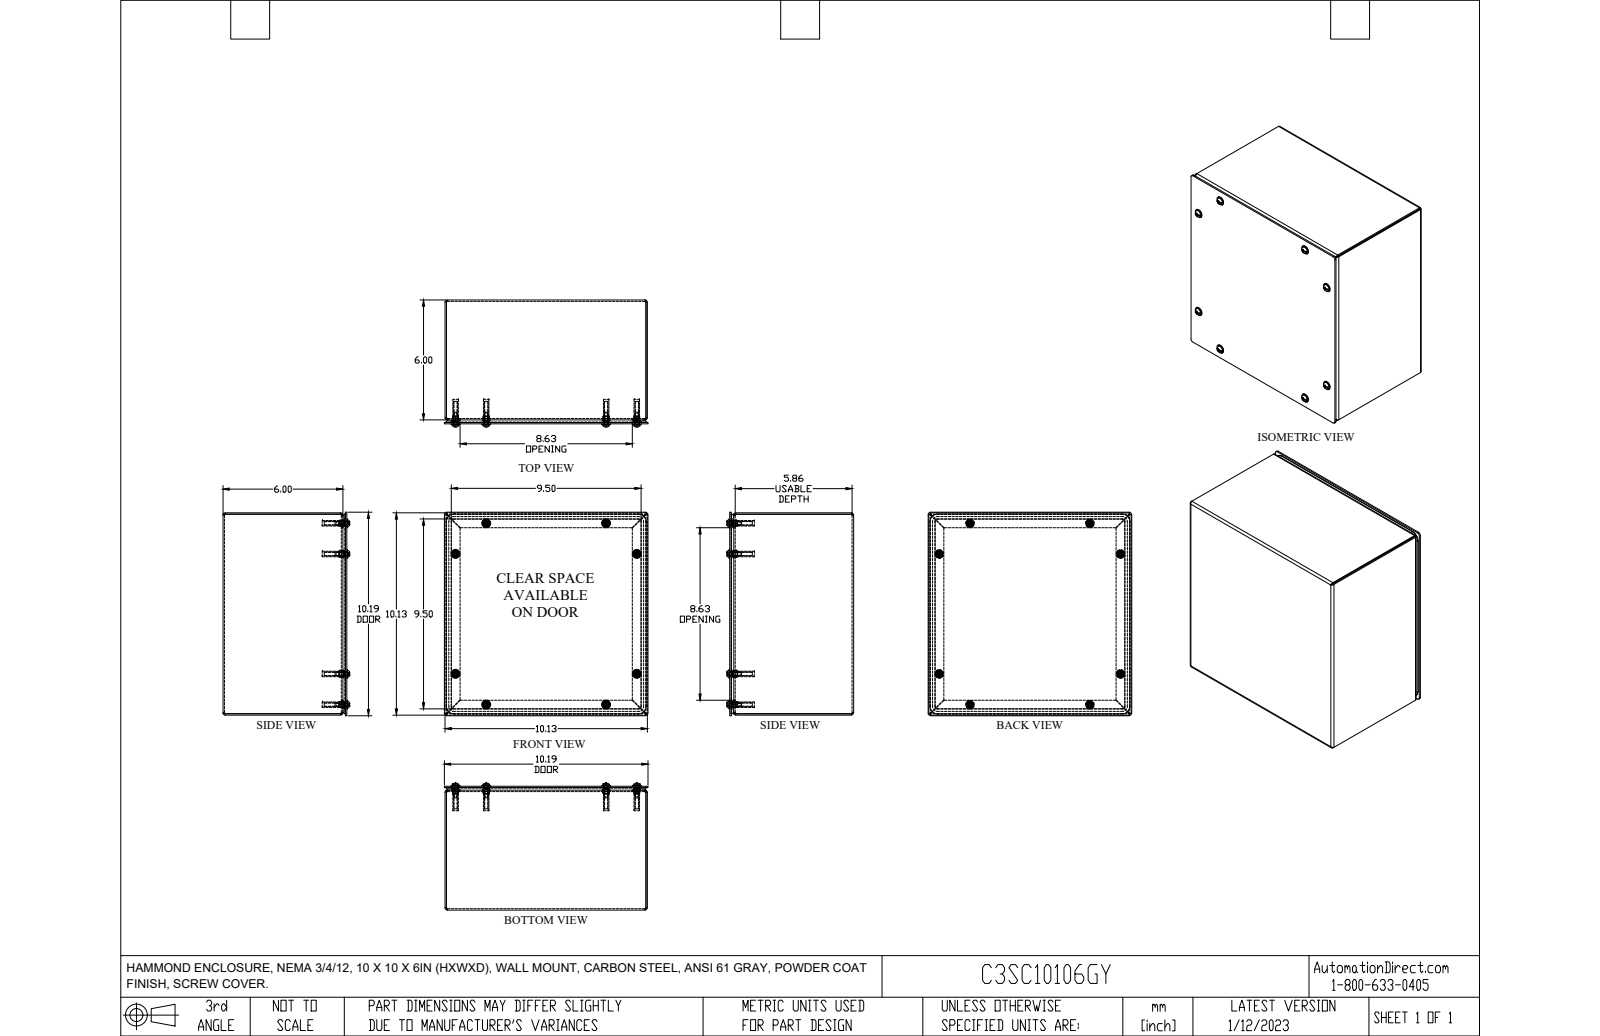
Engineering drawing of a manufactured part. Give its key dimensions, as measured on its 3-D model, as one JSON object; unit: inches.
{"part_name": "C3SC10106GY", "step_written_by": "SolidWorks 2021 (AUTOMOTIVE_DESIGN)", "units": "inches", "bodies": {"solids": 27, "faces": 780, "planar": 480, "cylindrical": 152, "other": 148}, "overall_size": [10.188, 10.188, 6.347], "volume_in3": 34.34, "surface_area_in2": 1007, "round_holes": [[0.159, 8], [0.16, 8], [0.25, 8]], "round_bosses_or_shafts": [[0.44, 8], [0.39, 8], [0.275, 8], [0.24, 8], [0.19, 8], [0.148, 8]], "partial_cylinders_radius": [[0.04, 8], [0.11, 8], [0.125, 8], [0.16, 8], [0.126, 4], [0.374, 4]], "face_to_face_distances": [0.07, 10.13, 10.06, 9.99, 10.06, 0.07, 0.072, 6.197, 6.125, 6.127], "hole_center_spacings": [7.693, 2.174, 6, 9.075, 10.659, 10.879]}
